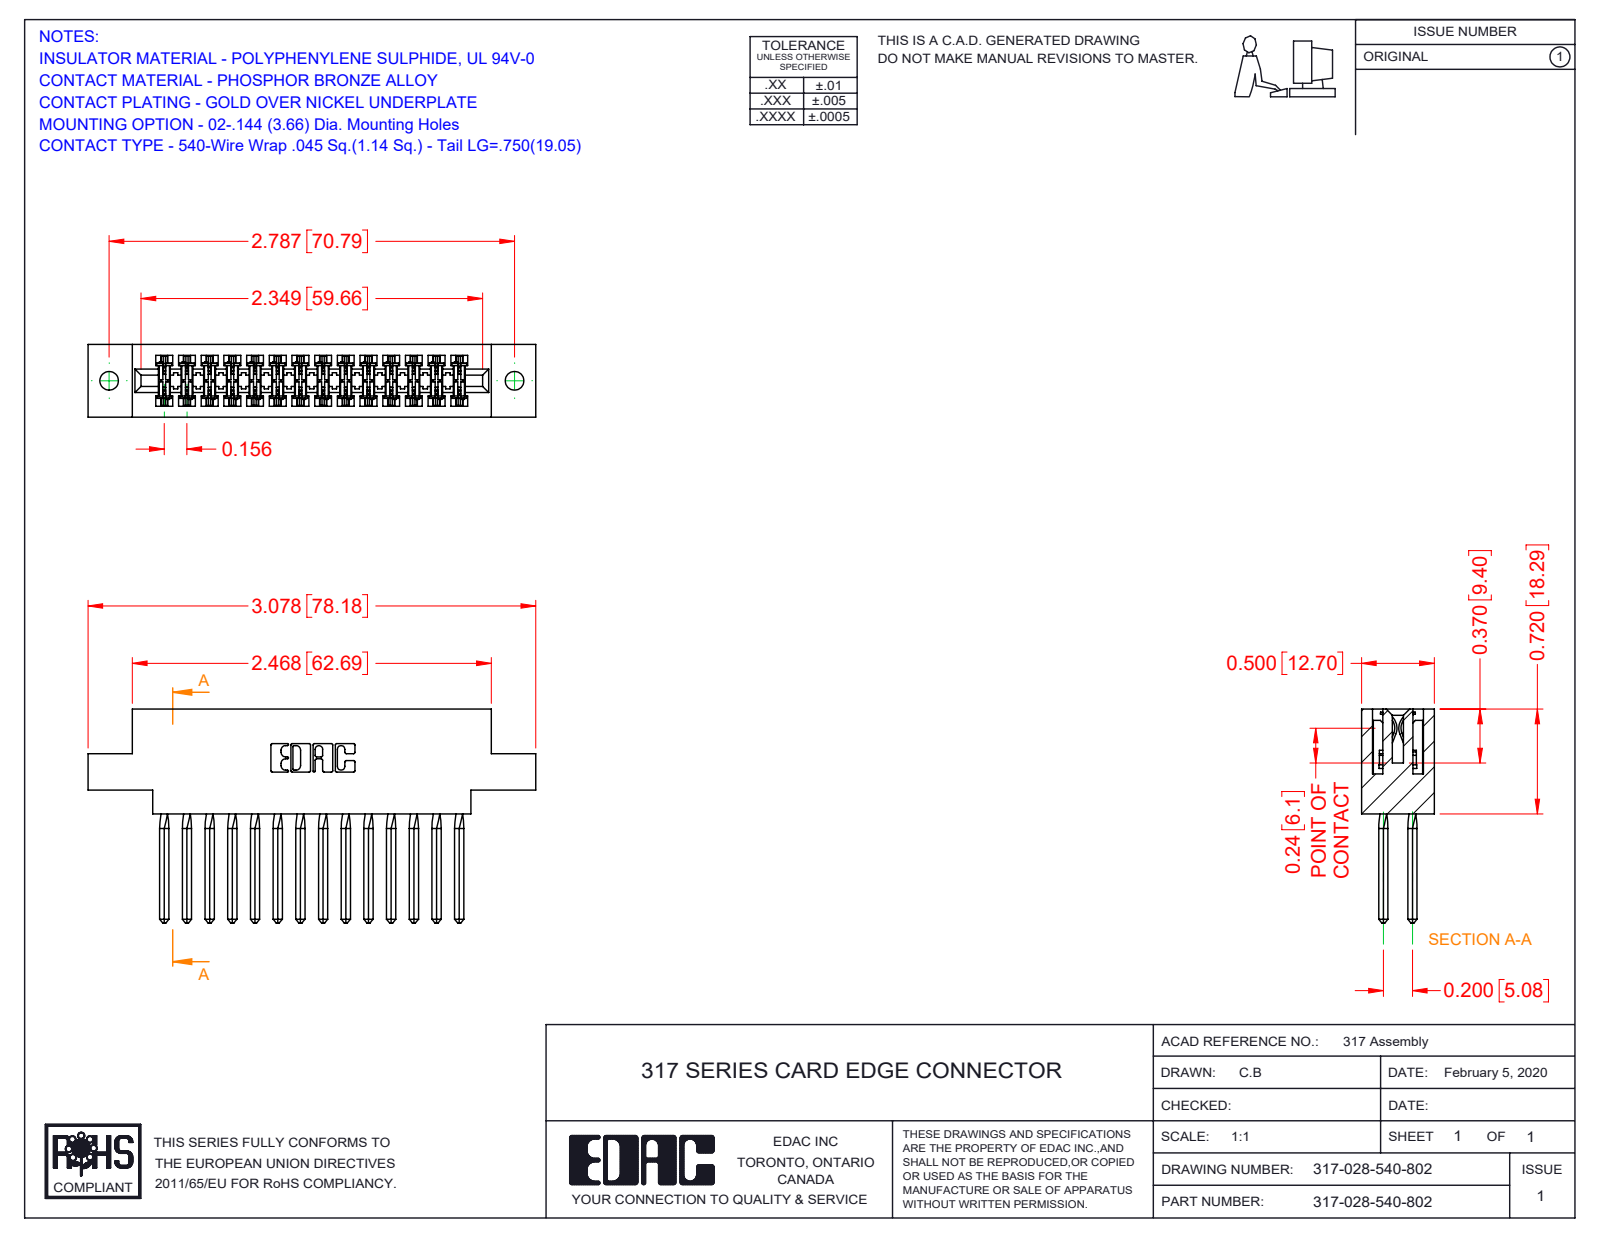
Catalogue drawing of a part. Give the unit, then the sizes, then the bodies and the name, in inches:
Units: inches
Overall size (bounding box): 3.078 × 1.47 × 0.5
Round holes (diameter × count): ⌀0.128 ×2
Partial cylindrical surfaces — rounded edges, fillets, slot ends (radius × count): R0.015 ×56, R0.01 ×22, R0.007 ×6, R0.031 ×6, R0.026 ×3, R0.095 ×2, R0.1 ×2, R0.11 ×2
Main face-to-face distances: 0.5, 0.075, 0.425, 0.11, 0.35, 0.22, 0.116, 0.72, 0.195, 0.331
Hole centre spacings: 2.787
Volume: 0.741 in³ · Surface area: 26 in²
Bodies: 29 solids, 2594 faces (2102 planar, 380 cylindrical, 112 other)
Part name (STEP PRODUCT): 317-290-001_540; 317 Part_.144 Dia; 317-028-540-802
STEP written by: SolidWorks 2016 (CONFIG_CONTROL_DESIGN)
